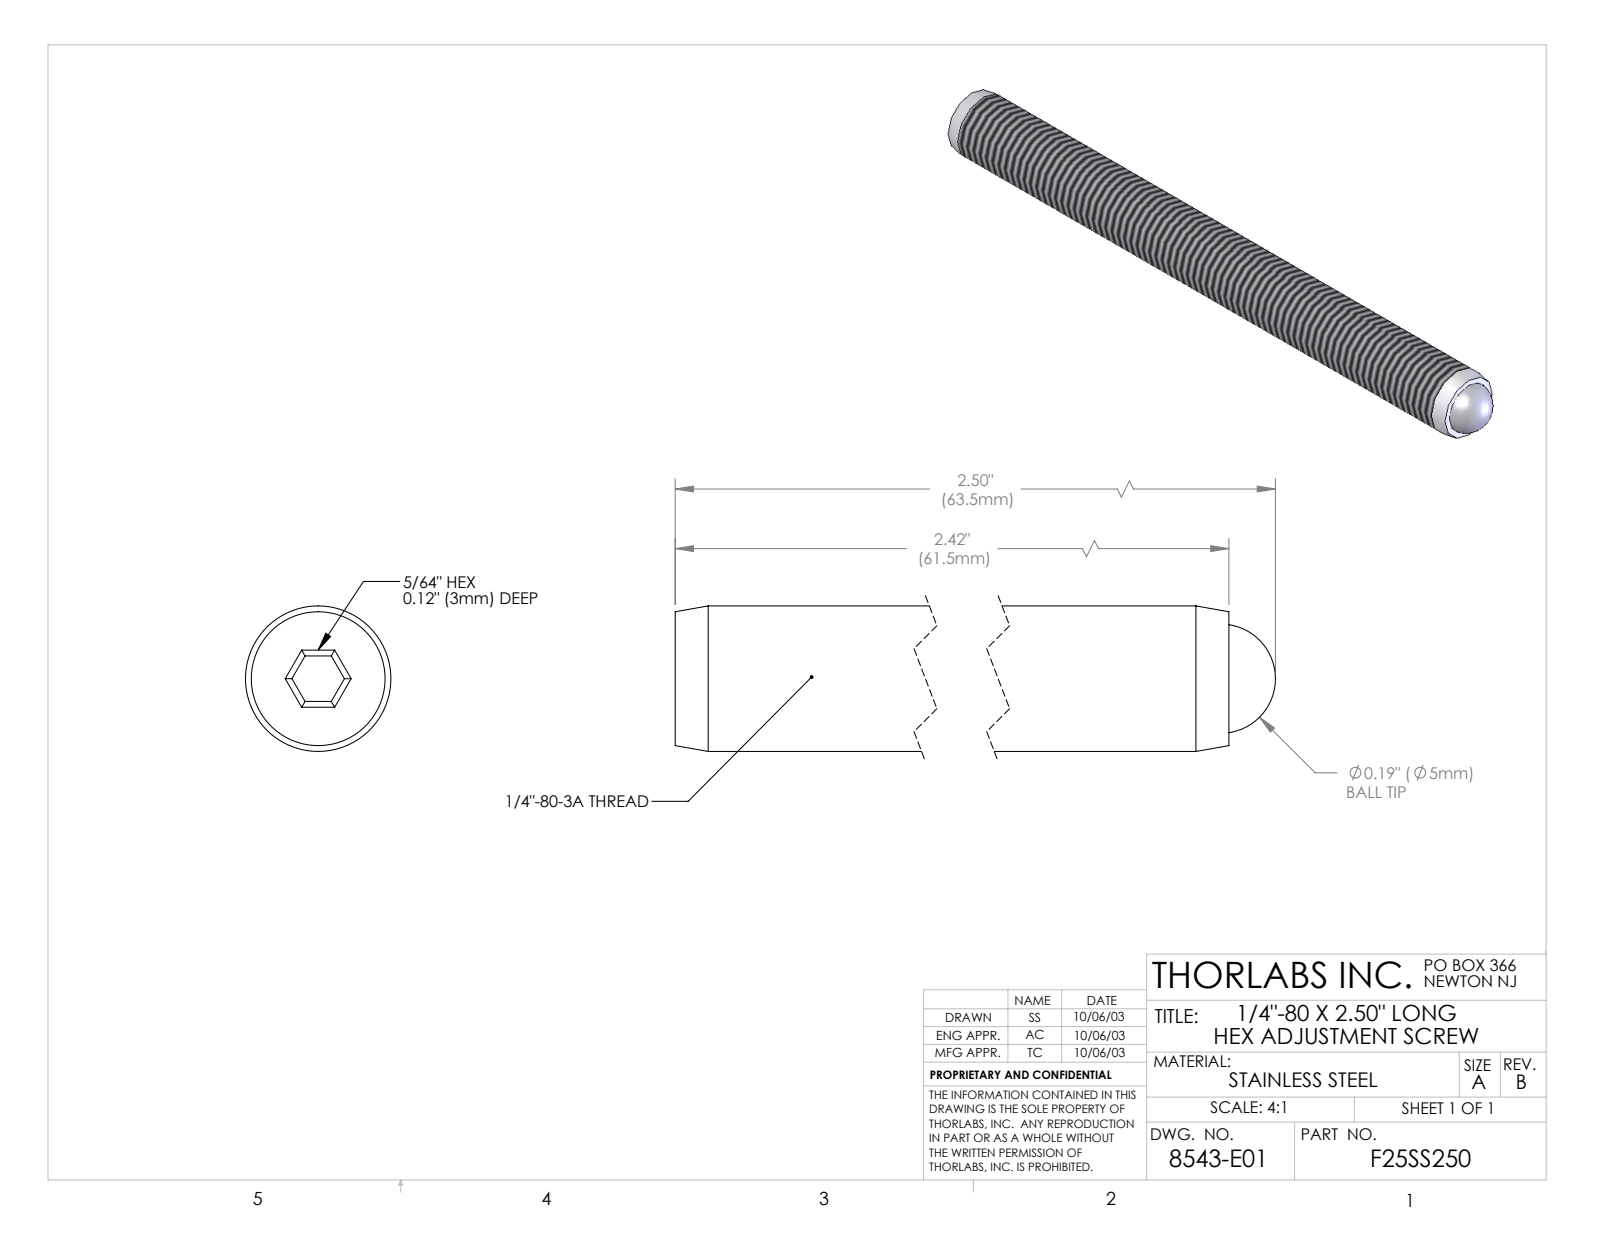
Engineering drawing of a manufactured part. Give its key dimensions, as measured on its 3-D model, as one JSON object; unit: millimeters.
{"part_name": "8543-E0W", "step_written_by": "SolidWorks 2007 (AUTOMOTIVE_DESIGN)", "units": "millimeters", "bodies": {"solids": 2, "faces": 29, "planar": 15, "cylindrical": 4, "other": 10}, "overall_size": [63.5, 6.35, 6.35], "volume_mm3": 1947, "surface_area_mm2": 1397, "round_holes": [[4.78, 1]], "round_bosses_or_shafts": [[6.35, 1]], "face_to_face_distances": [61.47, 1.99, 3.05, 58.42, 1.98]}
